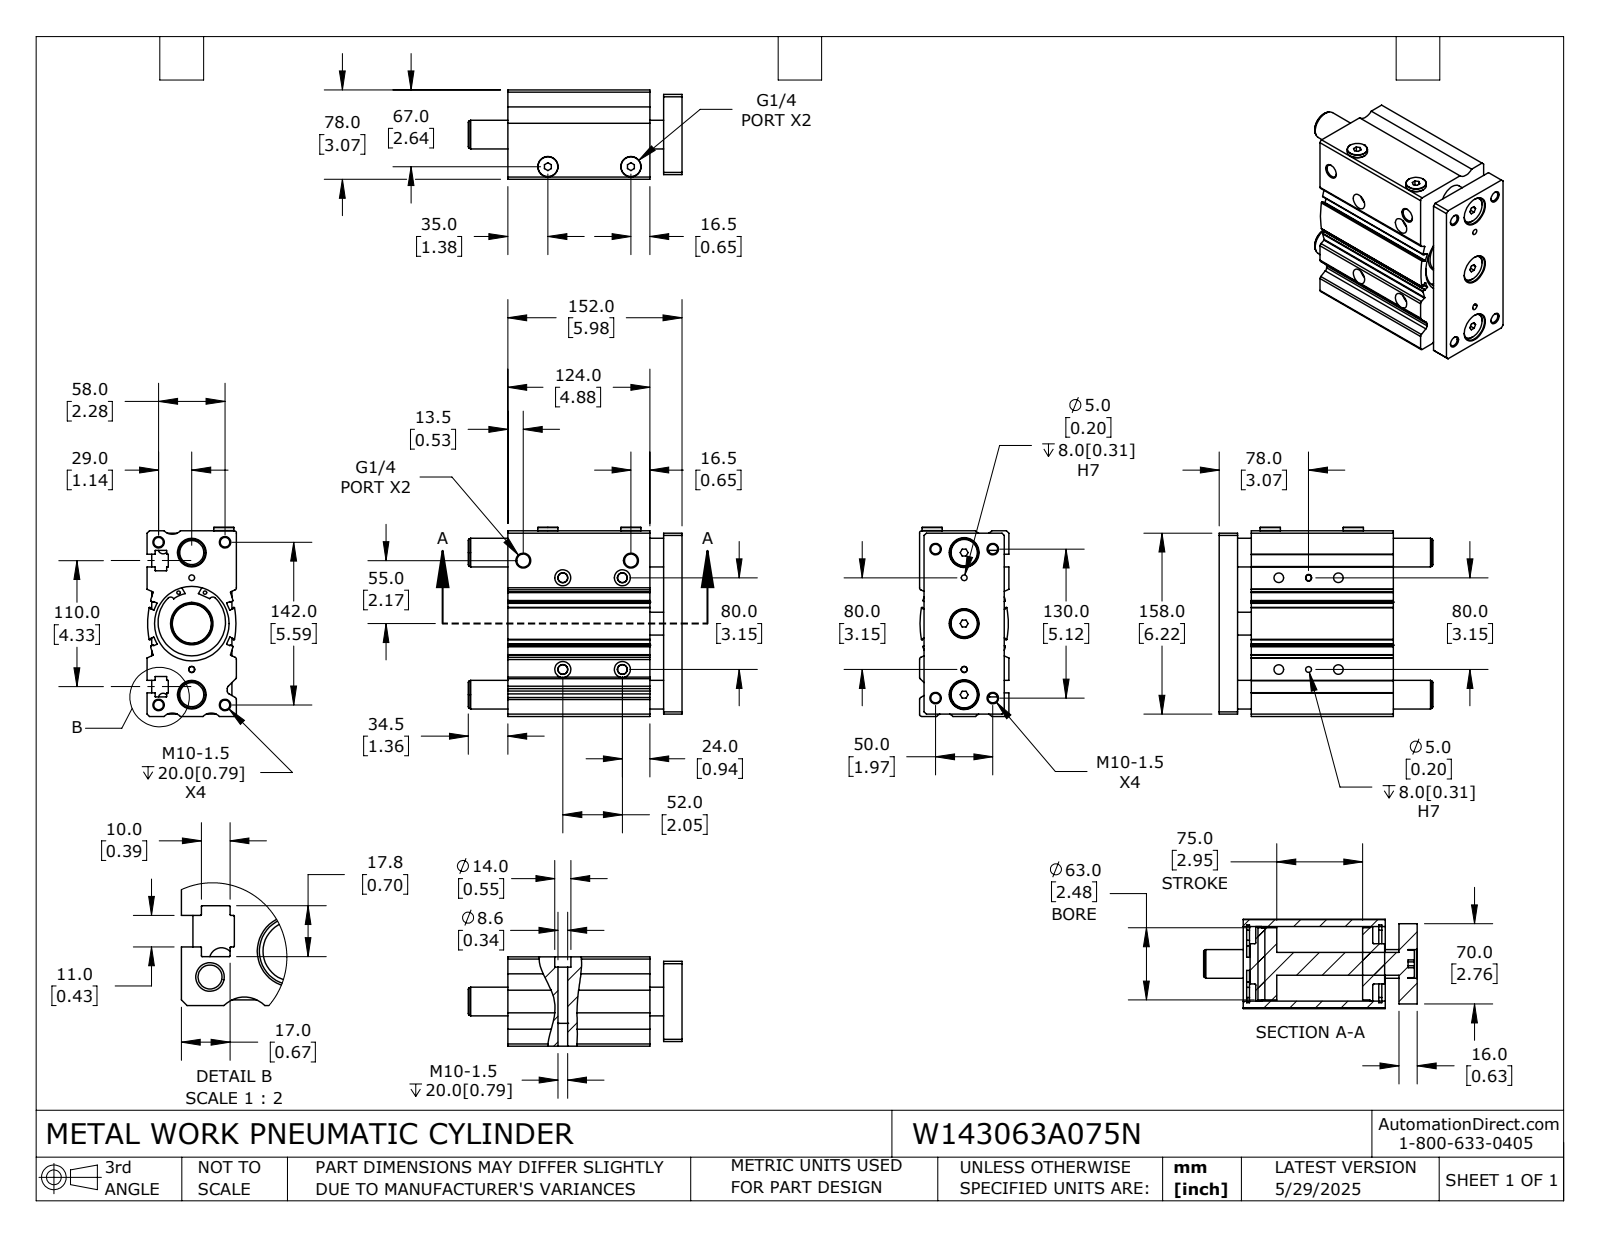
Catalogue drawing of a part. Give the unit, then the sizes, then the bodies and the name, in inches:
Units: inches
Overall size (bounding box): 7.343 × 6.496 × 3.071
Round holes (diameter × count): ⌀0.33 ×12, ⌀0.118 ×4, ⌀0.197 ×4, ⌀0.339 ×4, ⌀0.551 ×4, ⌀0.984 ×3, ⌀0.448 ×2, ⌀2.559 ×1
Round bosses / shafts (diameter × count): ⌀0.945 ×3, ⌀0.697 ×2, ⌀2.677 ×1, ⌀2.551 ×1, ⌀2.48 ×1, ⌀1.378 ×1, ⌀0.787 ×1
Partial cylindrical surfaces — rounded edges, fillets, slot ends (radius × count): R0.012 ×44, R0.02 ×12, R0.079 ×8, R0.098 ×4, R0.118 ×4, R0.394 ×3, R0.124 ×2, R1.157 ×2
Main face-to-face distances: 0.63, 3.071, 0.472, 1.102, 4.882, 5.984, 5.354, 6.378, 0.157, 2.913
Hole centre spacings: 0.284, 0.682, 0.991, 1.024, 1.158, 1.195, 1.392, 1.448
Volume: 82.92 in³ · Surface area: 392.1 in²
Bodies: 6 solids, 454 faces (182 planar, 216 cylindrical, 56 other)
Part name (STEP PRODUCT): W143063A075N_ROD; W143063A075N; W143063A075N_BODY
STEP written by: SolidWorks 2024 (CONFIG_CONTROL_DESIGN)
